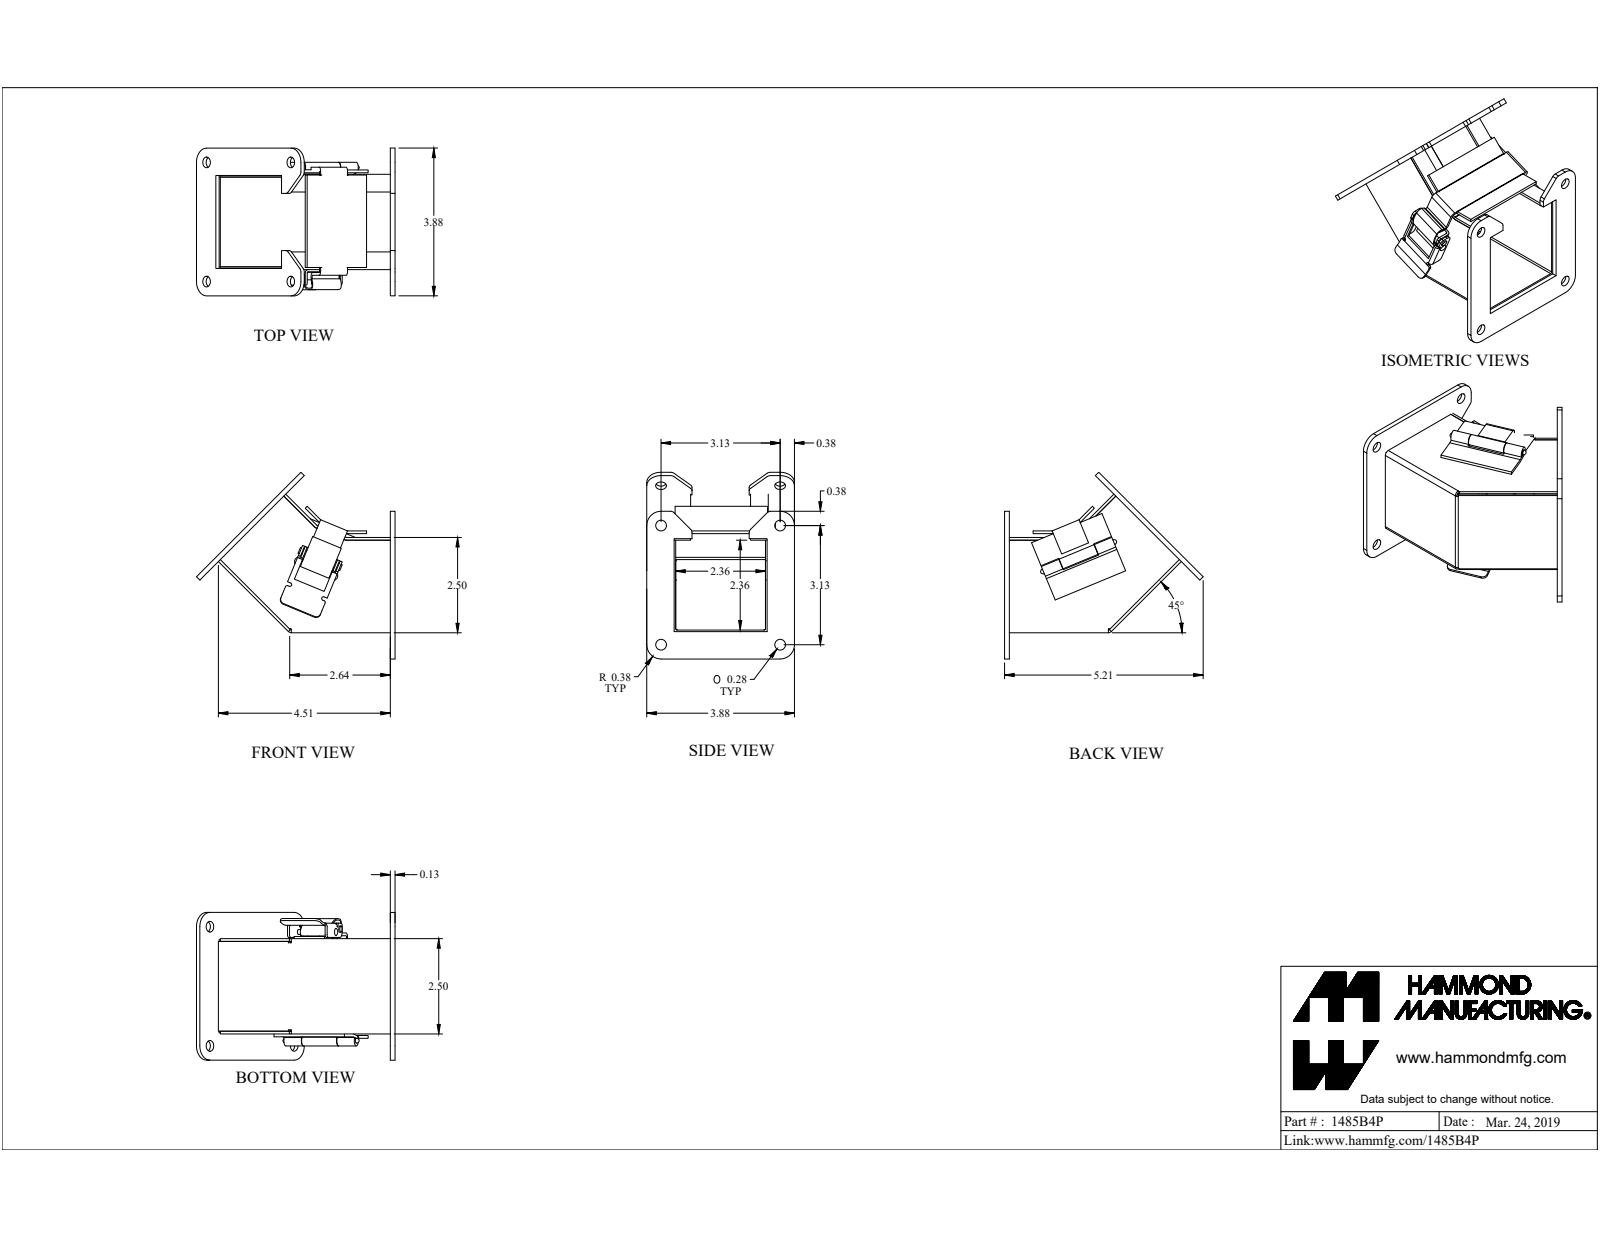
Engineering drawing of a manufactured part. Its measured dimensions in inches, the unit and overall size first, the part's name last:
Units: inches
Overall size (bounding box): 5.211 × 4.898 × 3.876
Round holes (diameter × count): ⌀0.281 ×8, ⌀0.125 ×2, ⌀0.164 ×2
Round bosses / shafts (diameter × count): ⌀0.162 ×2, ⌀0.158 ×2, ⌀0.275 ×1, ⌀0.275 ×1, ⌀0.125 ×1, ⌀0.125 ×1
Partial cylindrical surfaces — rounded edges, fillets, slot ends (radius × count): R0.125 ×12, R0.036 ×10, R0.108 ×10, R0.375 ×8, R0.029 ×4, R0.078 ×4, R0.086 ×4, R0.015 ×2
Main face-to-face distances: 0.072, 2.428, 0.125, 2.5, 2.356, 0.172, 0.244, 2.6, 2.6, 2.428
Hole centre spacings: 3.125, 2.928, 4.419, 4.419
Volume: 5.349 in³ · Surface area: 141.8 in²
Bodies: 12 solids, 292 faces (188 planar, 98 cylindrical, 6 other)
Part name (STEP PRODUCT): 1485B4P
STEP written by: SolidWorks 2019 (CONFIG_CONTROL_DESIGN)
